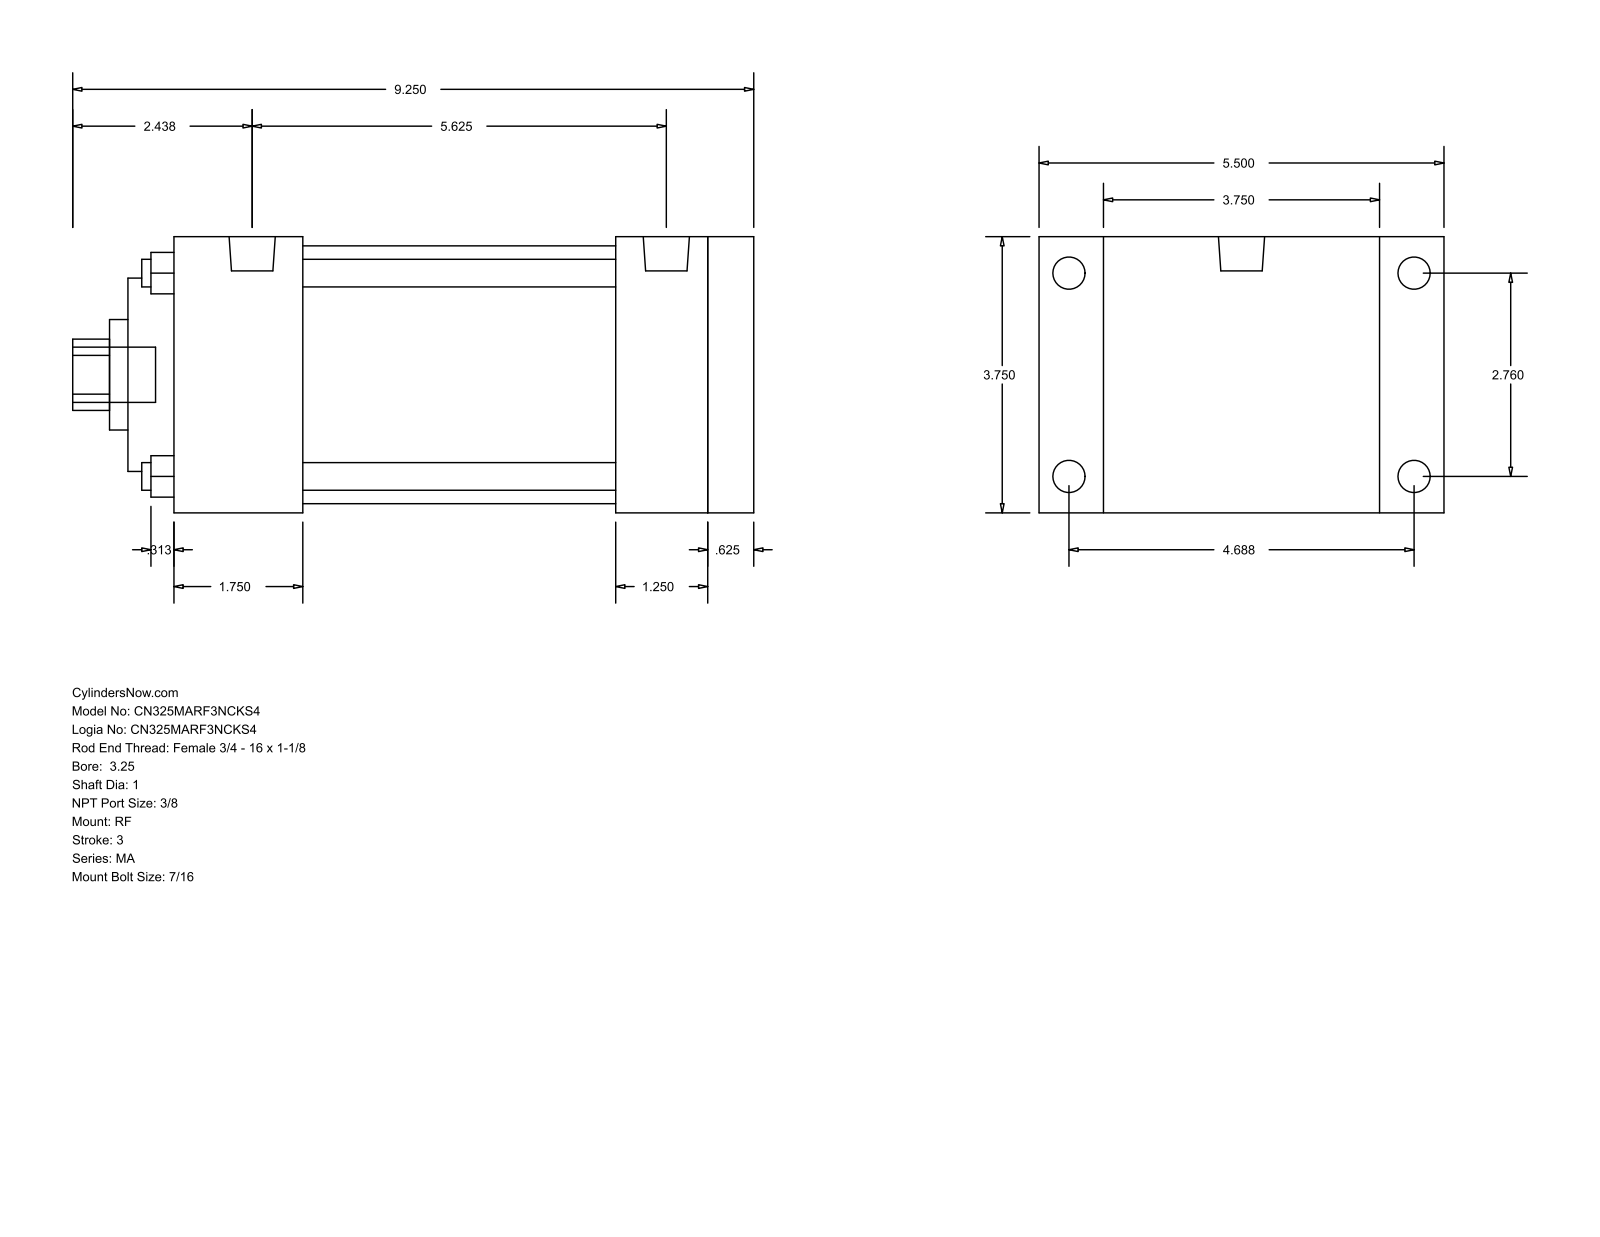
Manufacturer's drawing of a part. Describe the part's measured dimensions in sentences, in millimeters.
The part is named "MA_RF__0325_1". Its 3-D file was written by "GSSL Pune (CONFIG_CONTROL_DESIGN)". It is 0 solids with 94 faces: 65 planar, 29 cylindrical and 0 other. Overall it measures 234.95 by 139.7 by 95.25 millimeters. Round holes: 4 of diameter 9.53, 1 of diameter 25.4, 1 of diameter 38.1, 1 of diameter 66.67, 1 of diameter 88.9. Round bosses or shafts: 8 of diameter 11.11, 2 of diameter 15.93, 1 of diameter 19.05. Partial cylindrical surfaces (rounded edges, fillets, slot ends): 1 of radius 12.29. The main face-to-face distances are 95.24, 200.03, 184.15, 15.88, 22.23, 117.47, 15.87, 152.4, 31.75, 47.63. The hole center spacings are 49.57, 70.1, 99.14.
